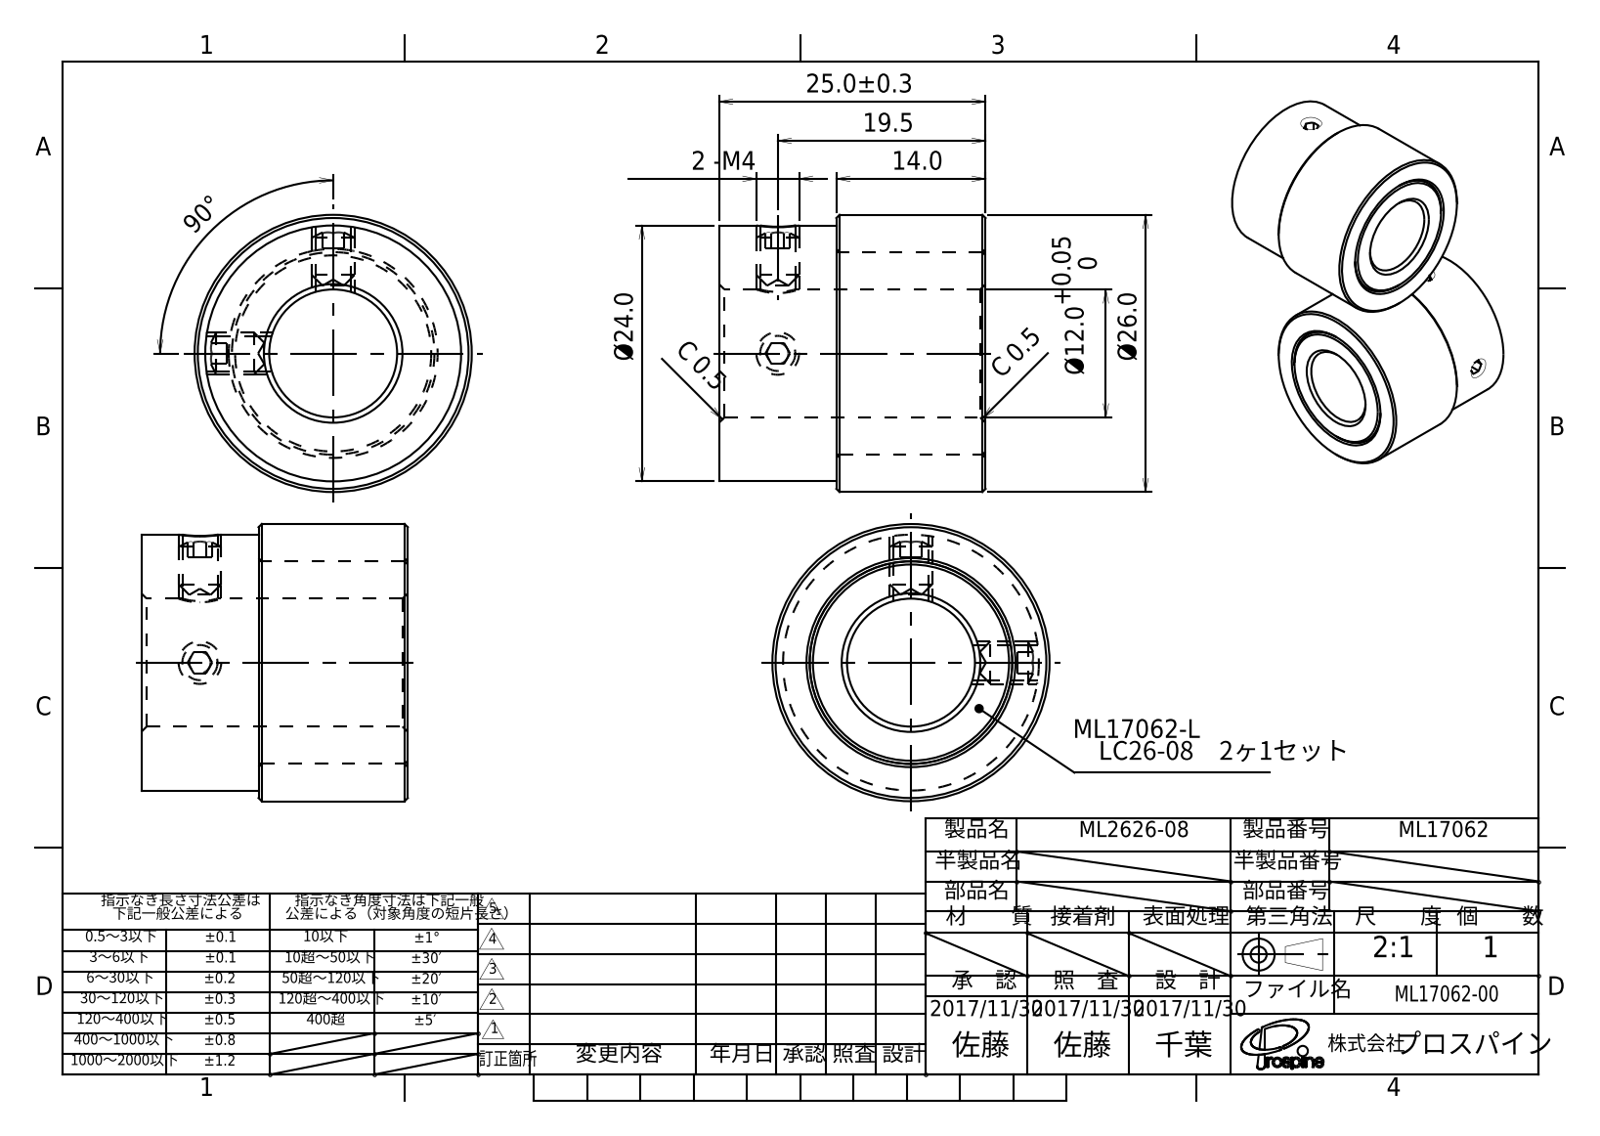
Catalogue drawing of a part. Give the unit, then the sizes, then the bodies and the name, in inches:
Units: inches
Overall size (bounding box): 2.165 × 1.22 × 1.22
Round holes (diameter × count): ⌀0.13 ×4, ⌀0.472 ×2, ⌀0.748 ×2
Round bosses / shafts (diameter × count): ⌀0.157 ×4, ⌀1.024 ×2, ⌀0.945 ×2
Main face-to-face distances: 0.551, 0.433, 0.984, 0.079, 0.117, 0.668, 0.236, 0.315, 1.101, 1.142
Hole centre spacings: 1.243, 0.696
Volume: 1.172 in³ · Surface area: 18.67 in²
Bodies: 10 solids, 104 faces (52 planar, 20 cylindrical, 32 other)
STEP written by: PSStep 10.0 (CONFIG_CONTROL_DESIGN)
